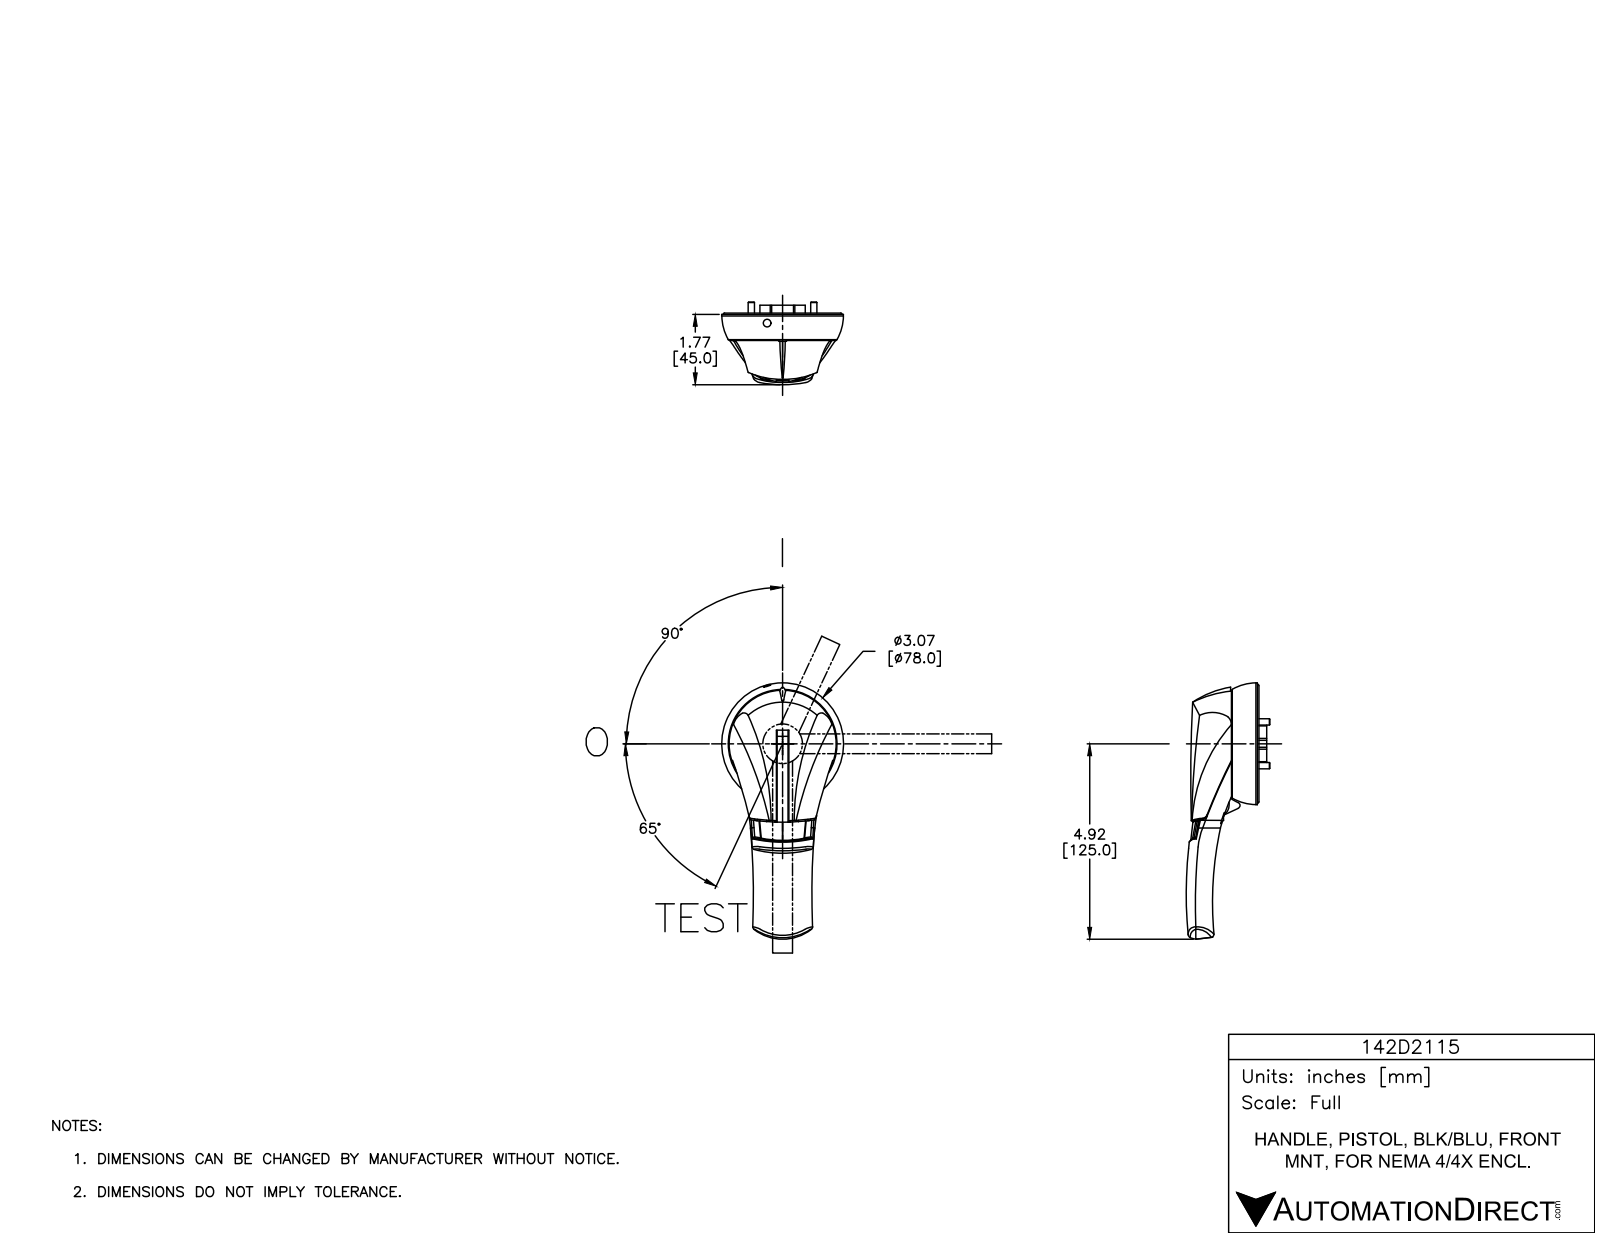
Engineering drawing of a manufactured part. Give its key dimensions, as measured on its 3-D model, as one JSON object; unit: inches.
{"part_name": "142D2115", "step_written_by": "SolidWorks 2015 (AUTOMOTIVE_DESIGN)", "units": "inches", "bodies": {"solids": 8, "faces": 1516, "planar": 810, "cylindrical": 548, "other": 158}, "overall_size": [6.458, 3.07, 2.079], "volume_in3": 9.514, "surface_area_in2": 87.32, "round_holes": [[0.157, 6], [0.339, 4], [0.425, 4], [0.03, 3], [0.169, 2], [0.362, 2], [0.118, 1], [0.189, 1], [2.992, 1]], "round_bosses_or_shafts": [[0.02, 11], [0.335, 4], [0.315, 4], [0.089, 3], [0.069, 3], [0.228, 2], [2.819, 1], [2.701, 1]], "partial_cylinders_radius": [[0.01, 221], [0.015, 20], [0.034, 20], [0.03, 15], [0.039, 4], [0.025, 3], [5.437, 3], [0.079, 2]], "face_to_face_distances": [0.024, 0.701, 0.713, 0.689, 0.035, 0.102, 0.276, 0.173, 0.244, 0.047], "hole_center_spacings": [0.961, 0.309, 0.669, 1.098, 1.102, 1.203, 1.575, 1.881]}
